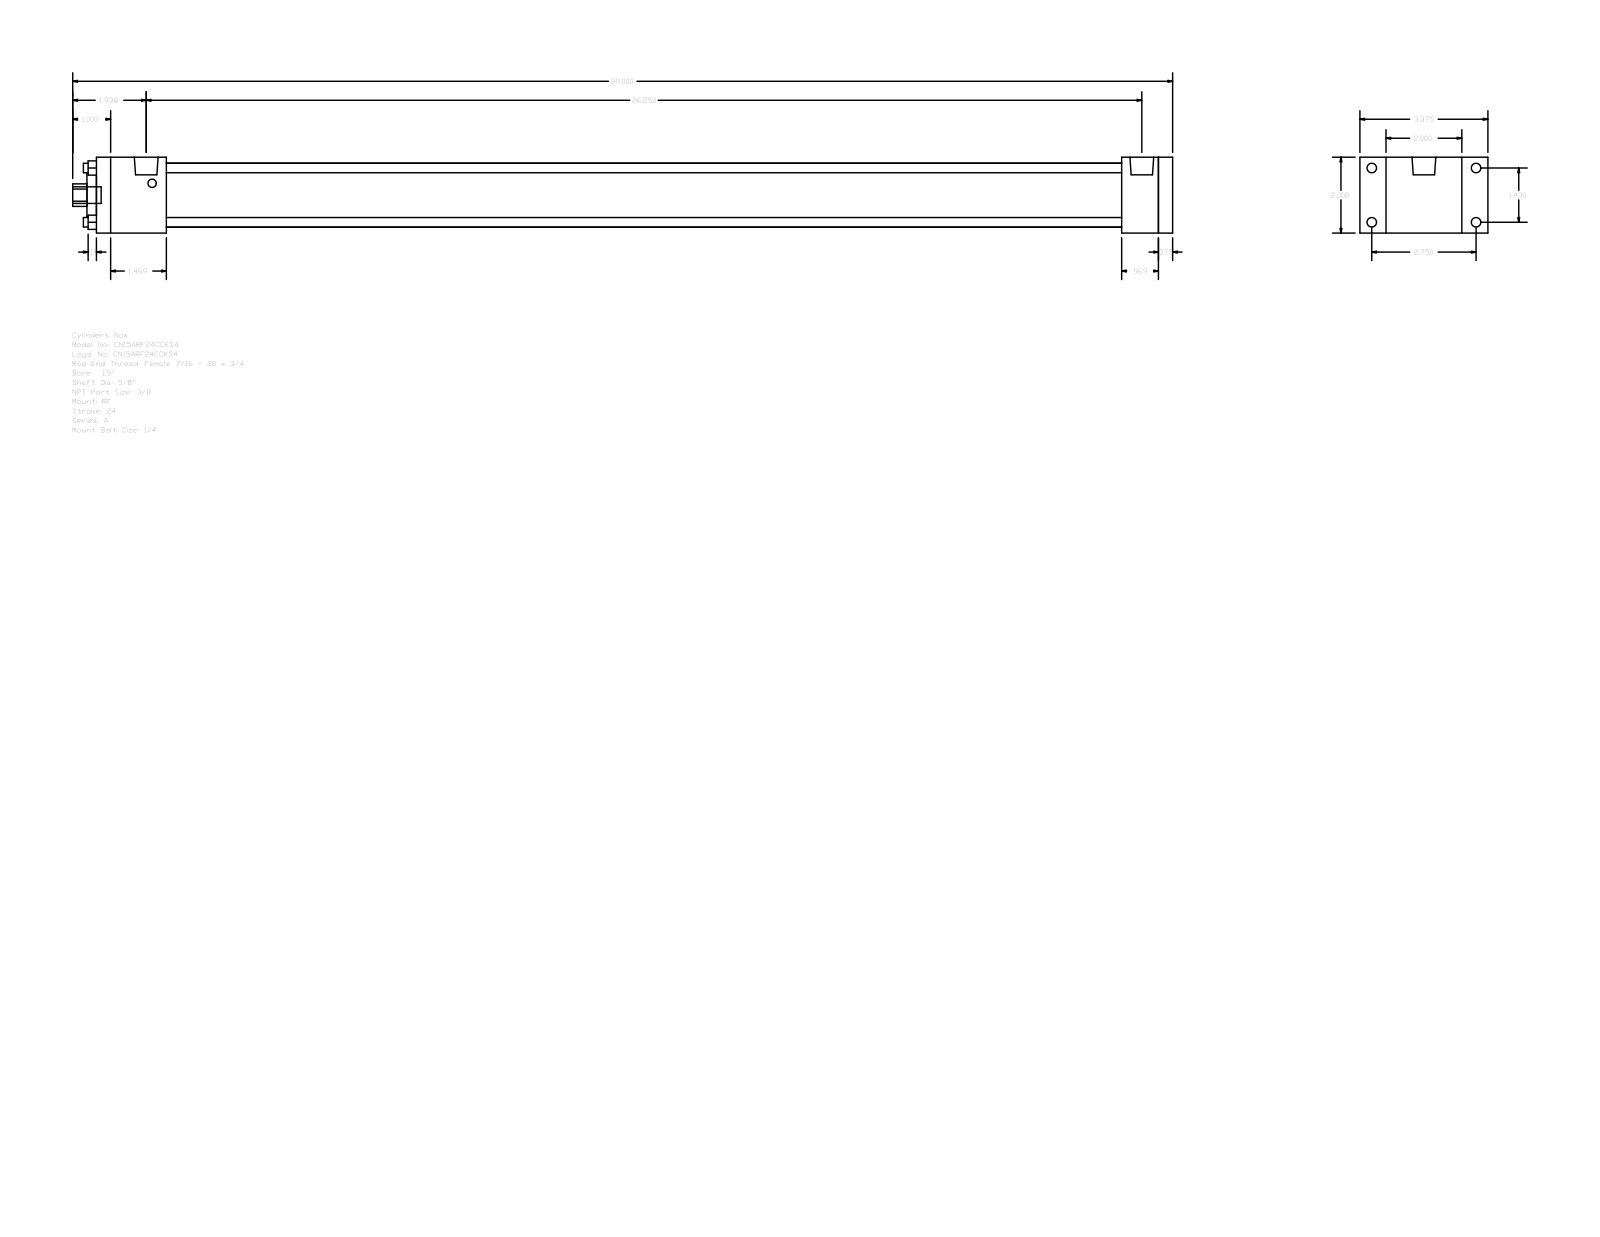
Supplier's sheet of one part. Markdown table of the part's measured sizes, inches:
| quantity | value |
| --- | --- |
| part name | A_RF__0150_0.625 |
| STEP written by | GSSL Pune (CONFIG_CONTROL_DESIGN) |
| units | inches |
| bodies | 0 solids, 92 faces (64 planar, 28 cylindrical, 0 other) |
| overall size | 29 × 3.375 × 2 |
| round holes (diameter × count) | 0.25 × 4, 0.625 × 1, 1.125 × 1, 1.69 × 1 |
| round bosses / shafts (diameter × count) | 0.25 × 4, 0.219 × 4, 0.627 × 2, 0.437 × 1 |
| partial cylindrical surfaces (radius × count) | 0.297 × 1 |
| main face-to-face distances | 2, 0.375, 28, 28.375, 27.031, 0.969, 1.344, 1.844, 25.187, 26.156 |
| hole center spacings | 1.011, 1.43, 2.022 |
